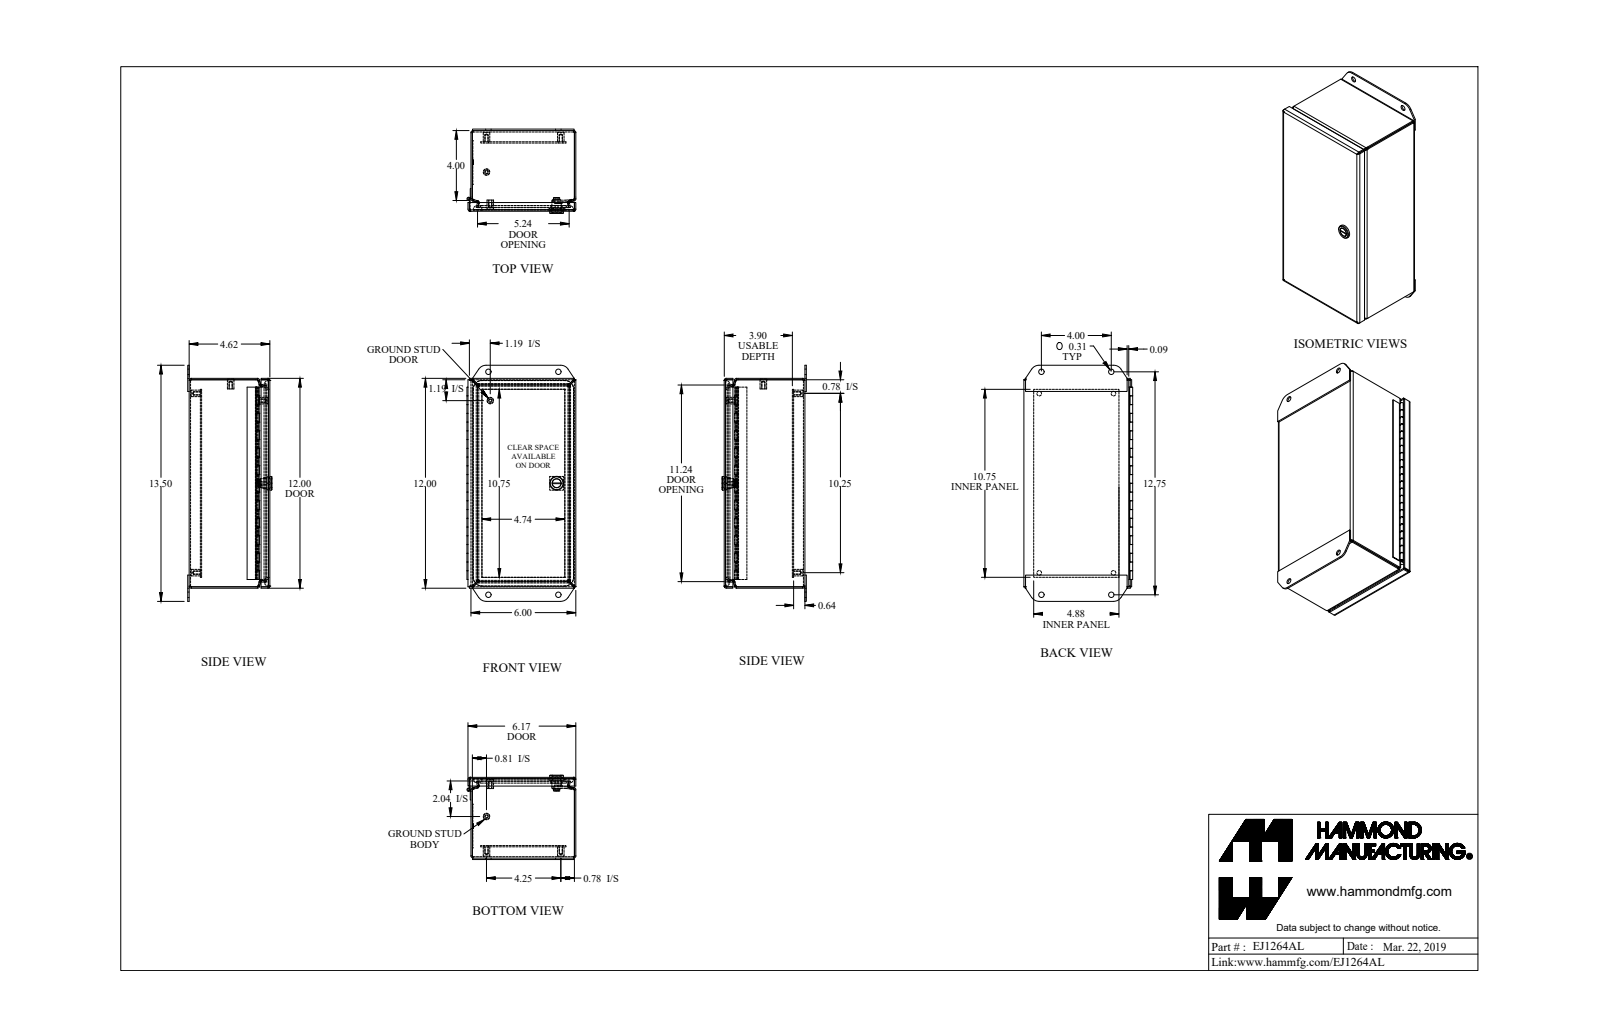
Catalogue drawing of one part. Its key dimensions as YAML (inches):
part_name: "EJ1264AL_Default"
step_written_by: "SolidWorks 2019 (CONFIG_CONTROL_DESIGN)"
units: inches
bodies: {solids: 14, faces: 658, planar: 432, cylindrical: 158, other: 68}
overall_size: [13.5, 6.226, 4.82]
volume: 35.36
surface_area: 906.7
round_holes:
  - {diameter: 0.159, count: 6}
  - {diameter: 0.265, count: 4}
  - {diameter: 0.313, count: 4}
  - {diameter: 0.516, count: 1}
round_bosses_or_shafts:
  - {diameter: 0.375, count: 6}
  - {diameter: 0.33, count: 6}
  - {diameter: 0.788, count: 1}
  - {diameter: 0.535, count: 1}
  - {diameter: 0.496, count: 1}
  - {diameter: 0.435, count: 1}
  - {diameter: 0.18, count: 1}
  - {diameter: 0.1, count: 1}
partial_cylinders:
  - {radius: 0.041, count: 16}
  - {radius: 0.121, count: 16}
  - {radius: 0.281, count: 12}
  - {radius: 0.25, count: 4}
  - {radius: 0.499, count: 4}
  - {radius: 0.5, count: 4}
  - {radius: 0.06, count: 2}
  - {radius: 0.03, count: 1}
face_to_face_distances: [0.081, 4.536, 5.919, 4.617, 4.455, 0.643, 3.974, 0.562, 3.893, 3.902]
hole_center_spacings: [0.024, 1.256, 4.25, 4.31, 11.501, 12.218, 4, 4.233]
